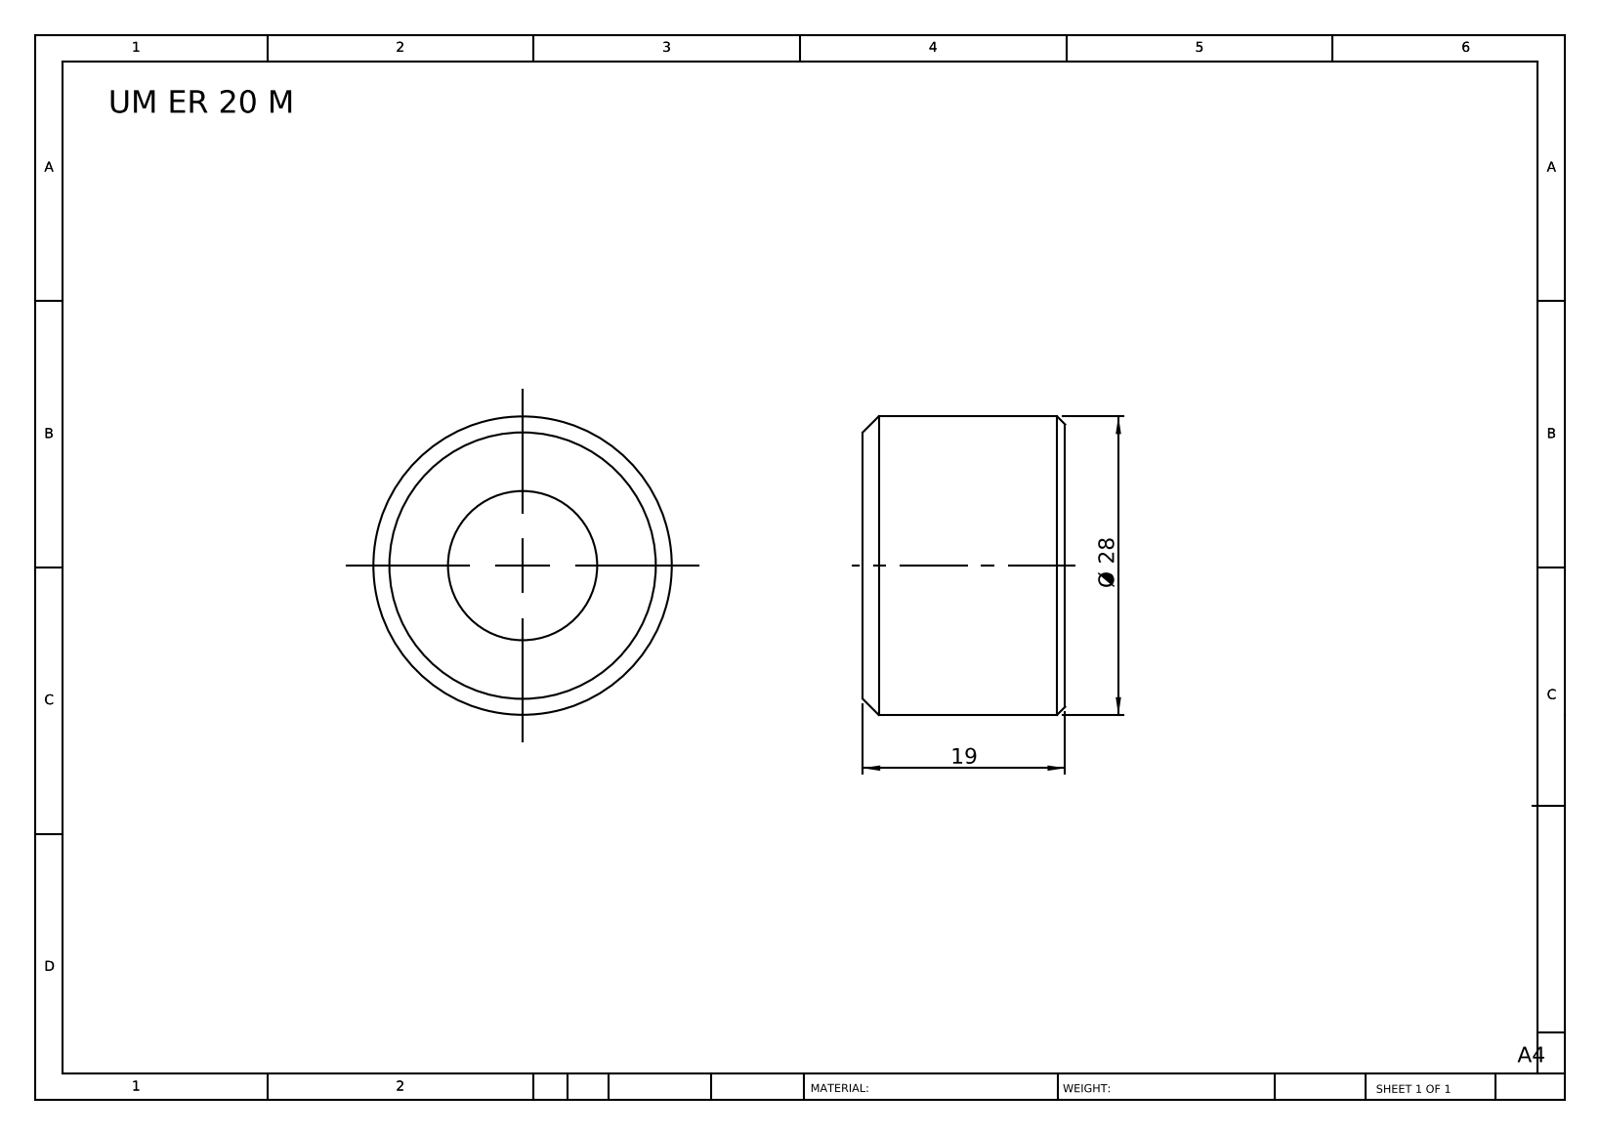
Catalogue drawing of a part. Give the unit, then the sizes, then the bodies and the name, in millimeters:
Units: millimetres
Overall size (bounding box): 28 × 28 × 19
Round holes (diameter × count): ⌀14 ×1
Round bosses / shafts (diameter × count): ⌀28 ×1
Main face-to-face distances: 19
Volume: 8 655 mm³ · Surface area: 3 311 mm²
Bodies: 1 solid, 10 faces (2 planar, 4 cylindrical, 4 other)
Part name (STEP PRODUCT): UM ER 20 M
STEP written by: SolidWorks 2014 (CONFIG_CONTROL_DESIGN)
